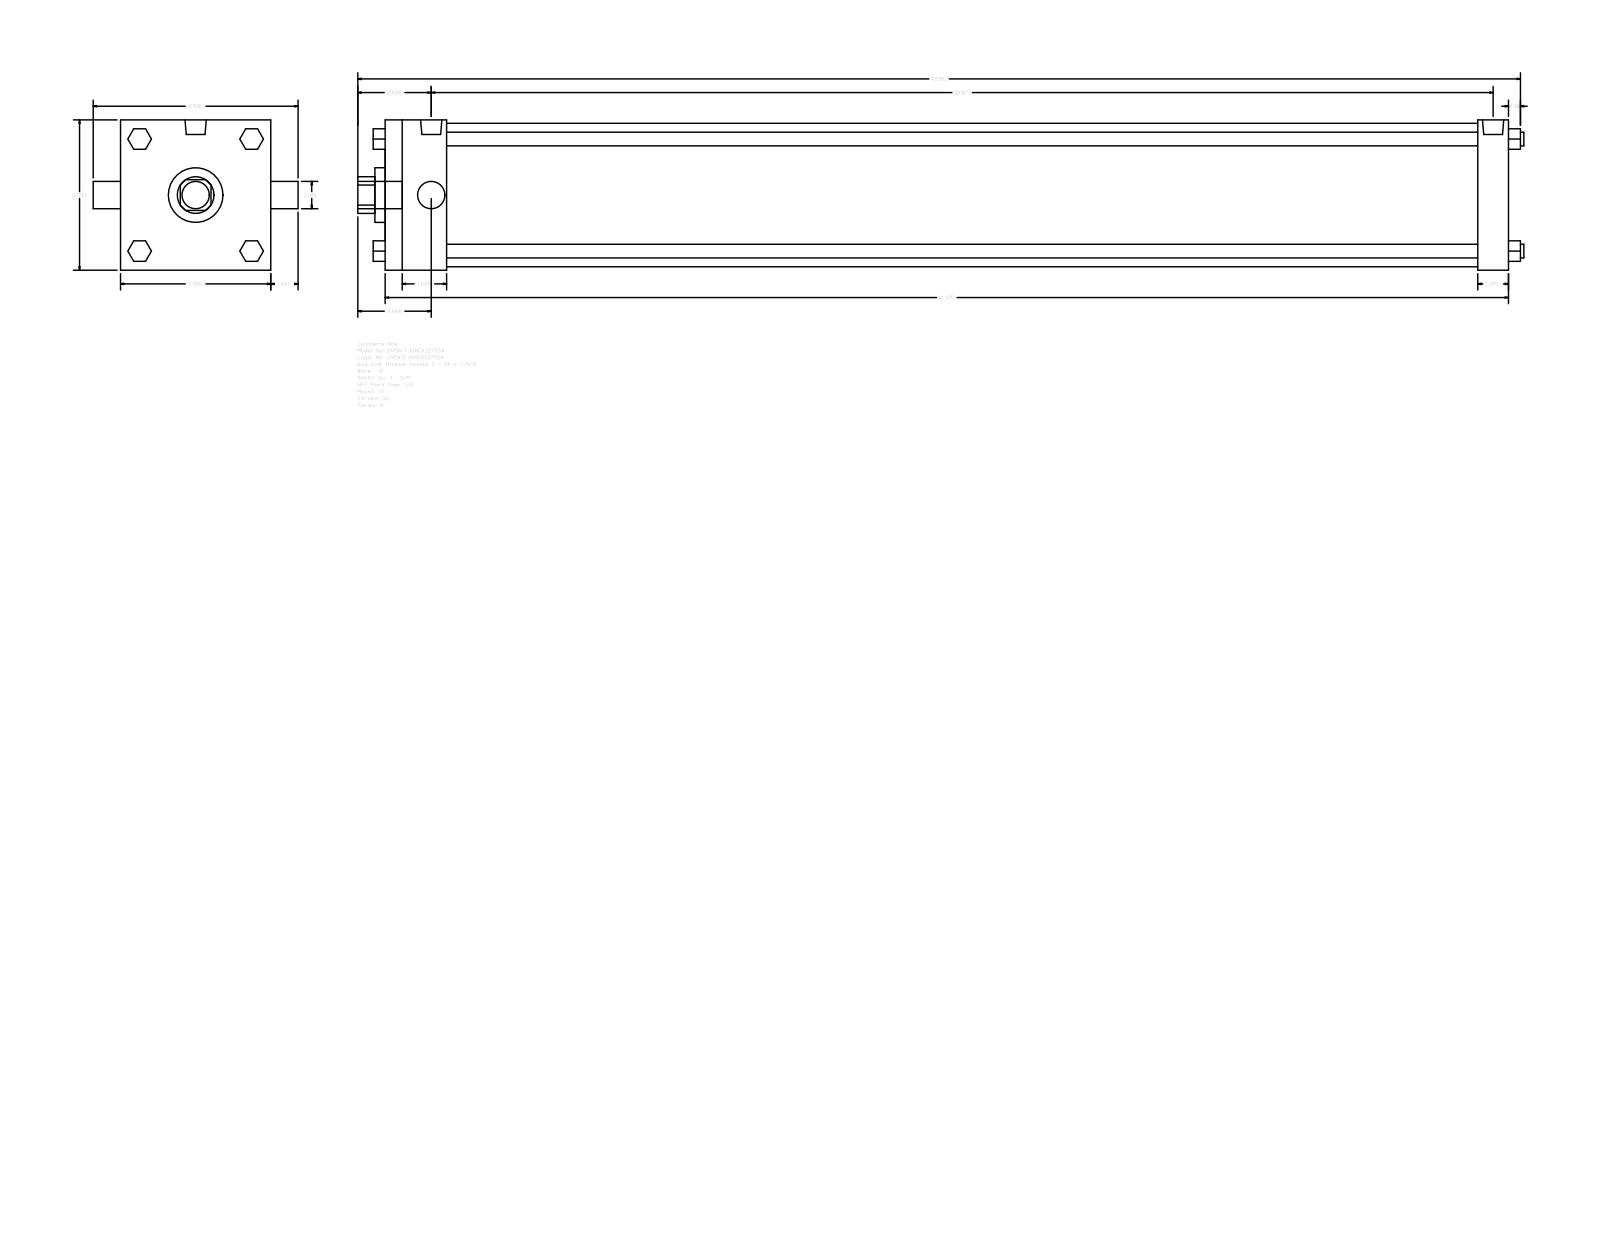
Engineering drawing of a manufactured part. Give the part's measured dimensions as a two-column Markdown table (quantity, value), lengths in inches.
| quantity | value |
| --- | --- |
| part name | A_TF__0500_1.375 |
| STEP written by | GSSL Pune (CONFIG_CONTROL_DESIGN) |
| units | inches |
| bodies | 0 solids, 120 faces (92 planar, 28 cylindrical, 0 other) |
| overall size | 42.687 × 7.5 × 5.5 |
| round holes (diameter × count) | 1 × 1, 1.375 × 1, 2 × 1, 5.25 × 1 |
| round bosses / shafts (diameter × count) | 0.5 × 4, 0.344 × 3, 0.778 × 2, 1 × 1 |
| partial cylindrical surfaces (radius × count) | 0.672 × 1 |
| main face-to-face distances | 5.5, 41.125, 1.125, 40, 2.25, 37.75, 38.875, 0.75, 2.05, 3.55 |
